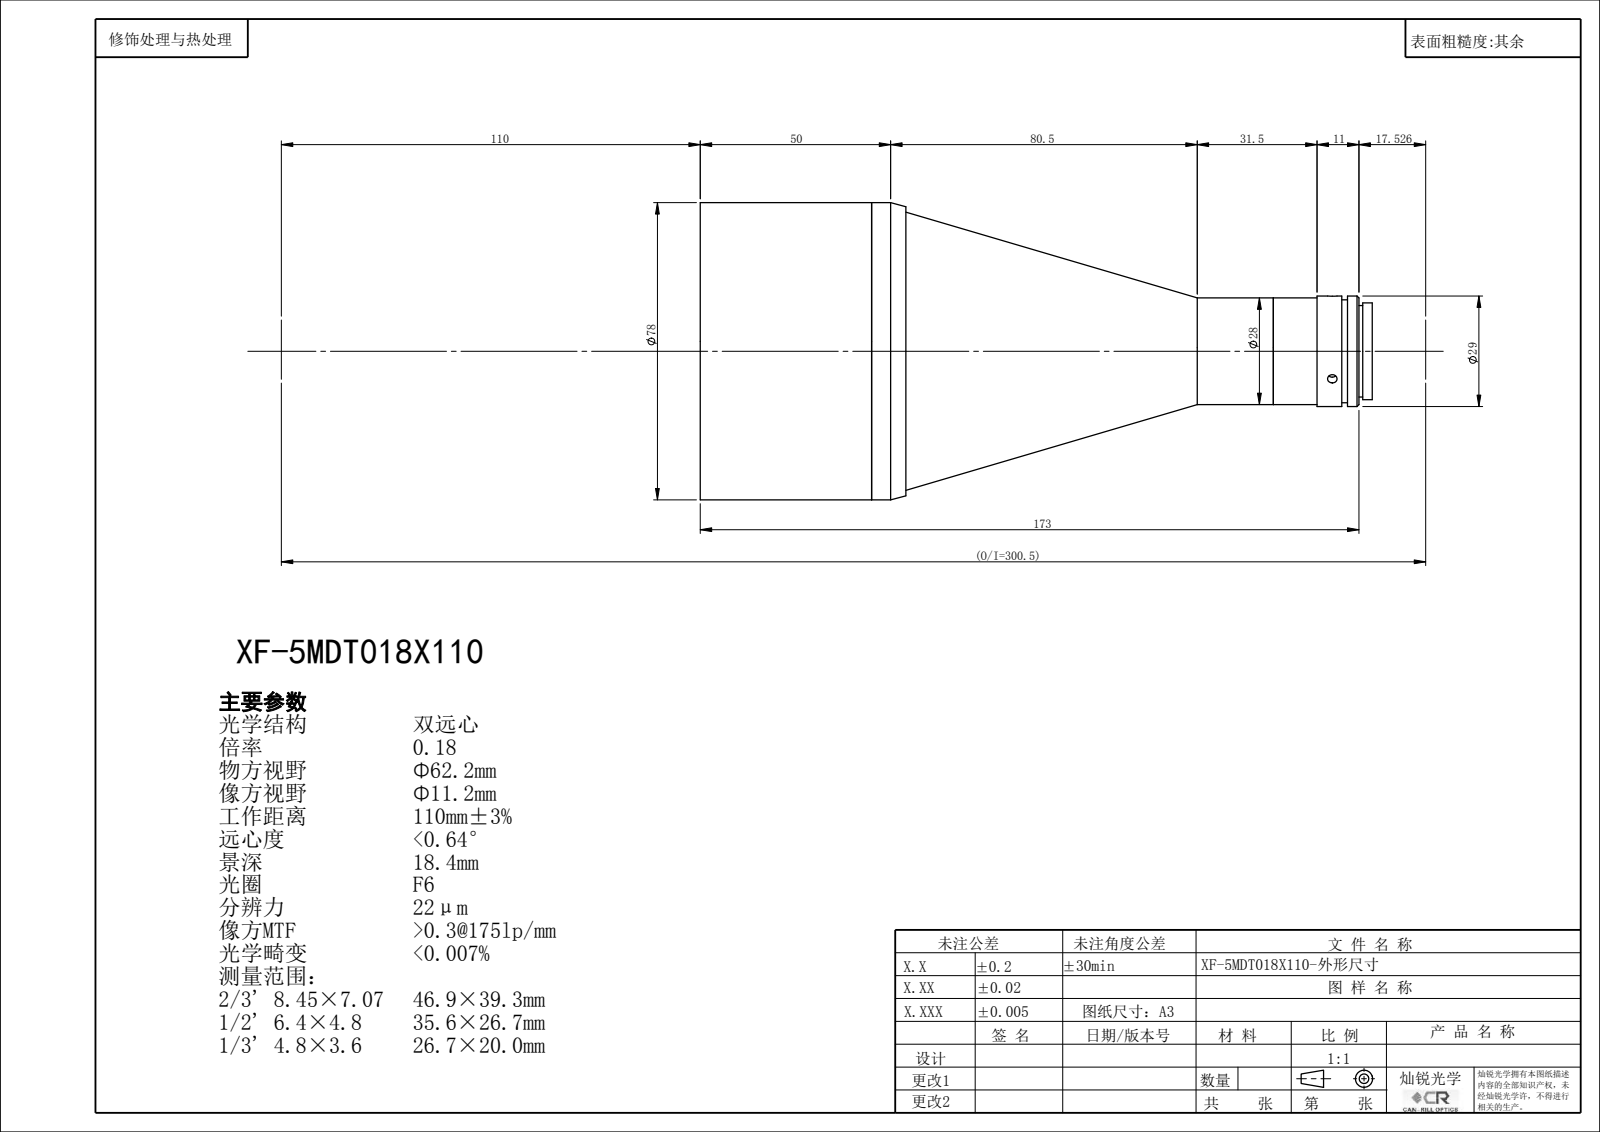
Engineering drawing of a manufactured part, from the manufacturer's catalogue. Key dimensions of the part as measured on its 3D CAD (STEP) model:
Part name (STEP PRODUCT): XF-5MDT018X110
STEP written by: SolidWorks 2014 (CONFIG_CONTROL_DESIGN)
Units: millimetres
Bodies: 0 solids, 74 faces (26 planar, 38 cylindrical, 10 other)
Overall size (bounding box): 176.47 × 78 × 78
Round holes (diameter × count): ⌀2.5 ×3, ⌀16 ×1, ⌀18.4 ×1, ⌀21.4 ×1, ⌀70 ×1, ⌀73 ×1
Round bosses / shafts (diameter × count): ⌀78 ×1, ⌀29 ×1, ⌀28 ×1, ⌀27 ×1, ⌀25.4 ×1, ⌀24 ×1, ⌀20 ×1
Main face-to-face distances: 45, 2.2, 42.8, 54, 51.8, 9, 161.97, 159.77, 116.97, 107.97
